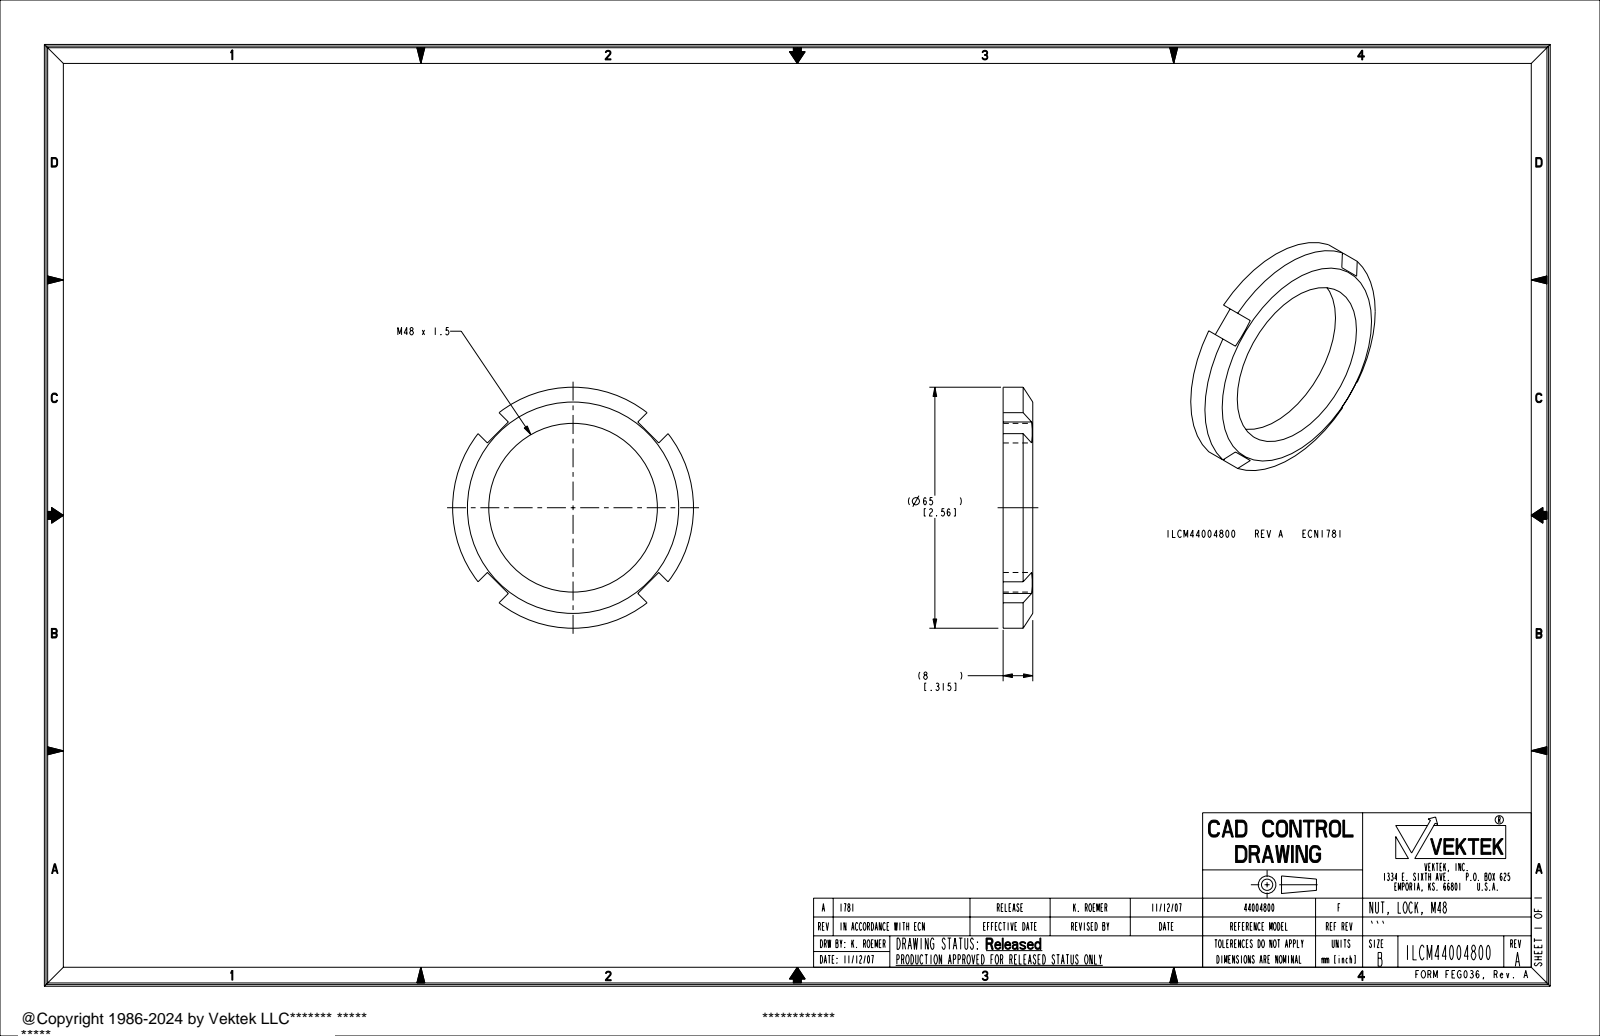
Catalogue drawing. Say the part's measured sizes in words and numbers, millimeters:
The part is named "ILCM44004800". Its 3-D file was written by "PRO/ENGINEER BY PARAMETRIC TECHNOLOGY CORPORATION, 2005180 (AUTOMOTIVE_DESIGN_CC2)". It is 1 solid with 22 faces: 14 planar, 6 cylindrical and 2 other. Overall it measures 65 by 65 by 8 millimeters. Its volume is 11 735 cubic millimeters and its surface area 5 781 square millimeters. Round holes: 1 of diameter 45.5. Round bosses or shafts: 1 of diameter 65. The main face-to-face distances are 8, 32.7, 24.7, 57.4.
